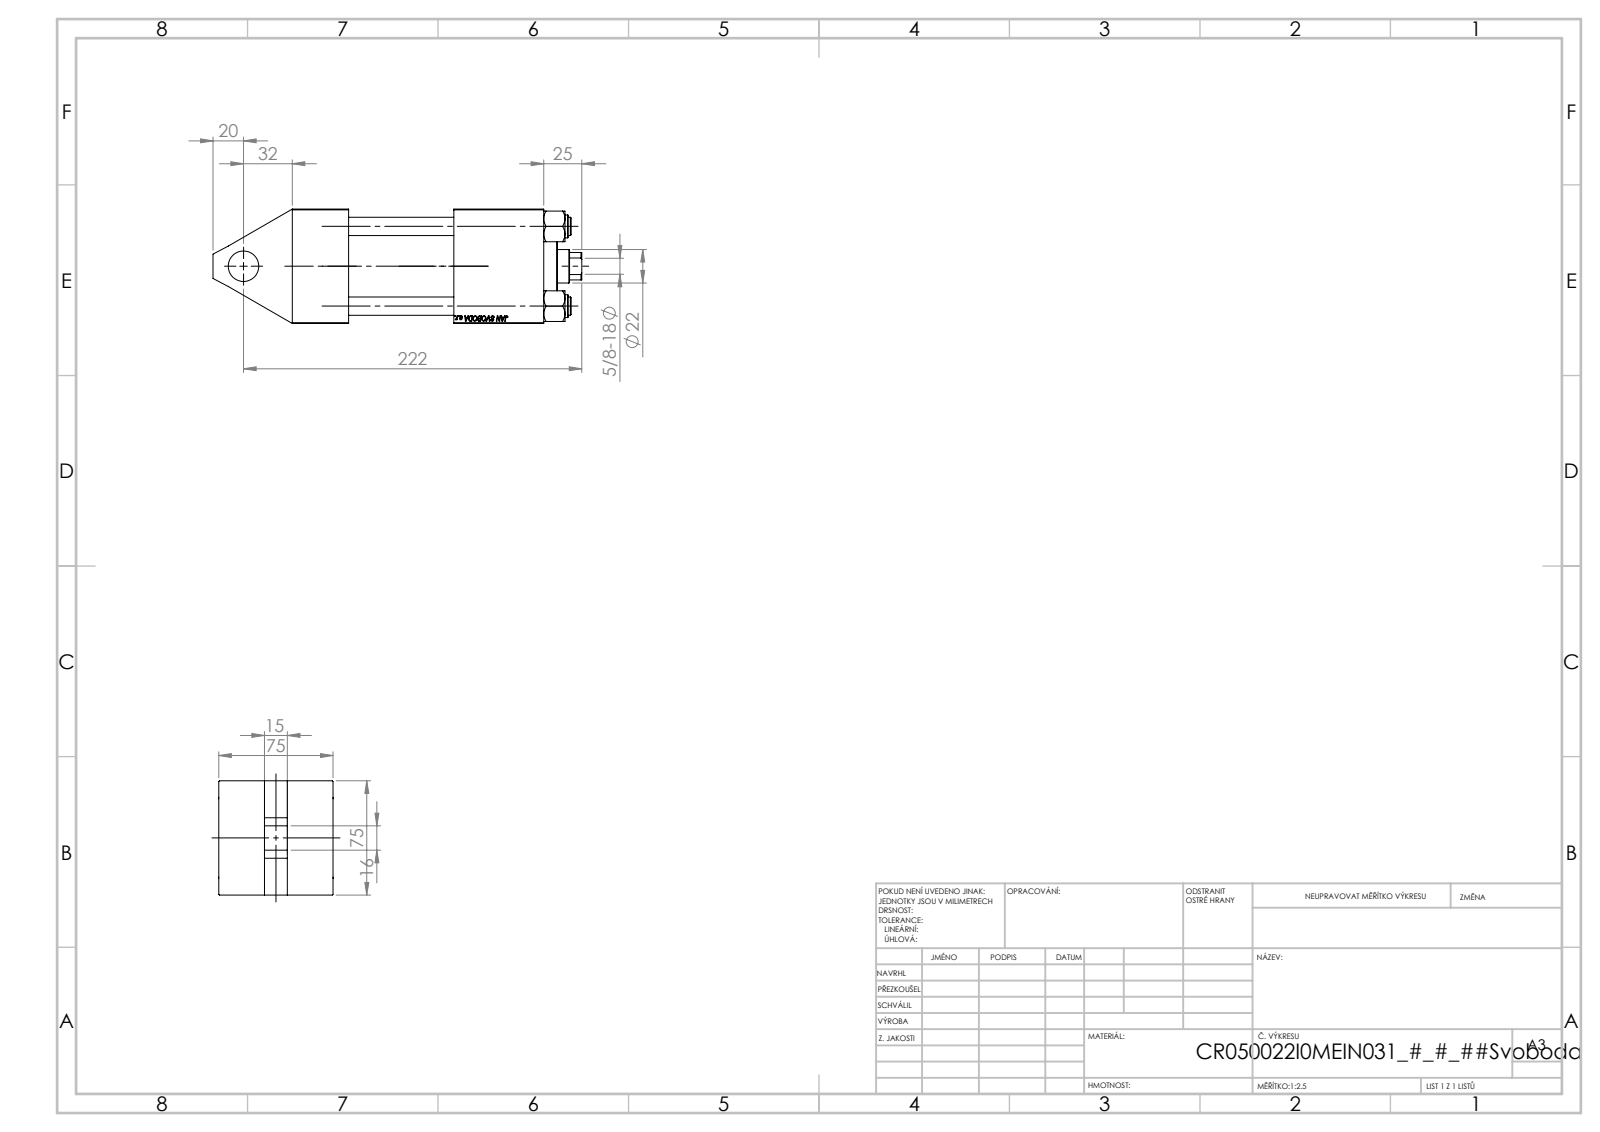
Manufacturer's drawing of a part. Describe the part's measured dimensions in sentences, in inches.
The part is named "V215CR_TYCINKA_I; V215CR_VCP_I; NUT_M5_I; V215CR_I_Body (+1 more)". Its 3-D file was written by "SolidWorks 2019 (CONFIG_CONTROL_DESIGN)". It is 11 solids with 1078 faces: 502 planar, 80 cylindrical and 496 other. Overall it measures 9.528 by 2.974 by 2.953 inches. Its volume is 43.61 cubic inches and its surface area 251.5 square inches. Round holes: 4 of diameter 0.472, 2 of diameter 0.276, 2 of diameter 0.825, 2 of diameter 1.181, 1 of diameter 0.413, 1 of diameter 0.787, 1 of diameter 0.866, 1 of diameter 0.984, 1 of diameter 1.614, 1 of diameter 1.969, 1 of diameter 2.087. Round bosses or shafts: 4 of diameter 0.591, 1 of diameter 2.205, 1 of diameter 1.339. Partial cylindrical surfaces (rounded edges, fillets, slot ends): 1 of radius 0.413. The main face-to-face distances are 2.953, 5.039, 1.457, 6.496, 1.772, 1.181, 4.173, 2.717, 2.323, 5.366. The hole center spacings are 1.456, 2.059, 2.912, 4.114.
